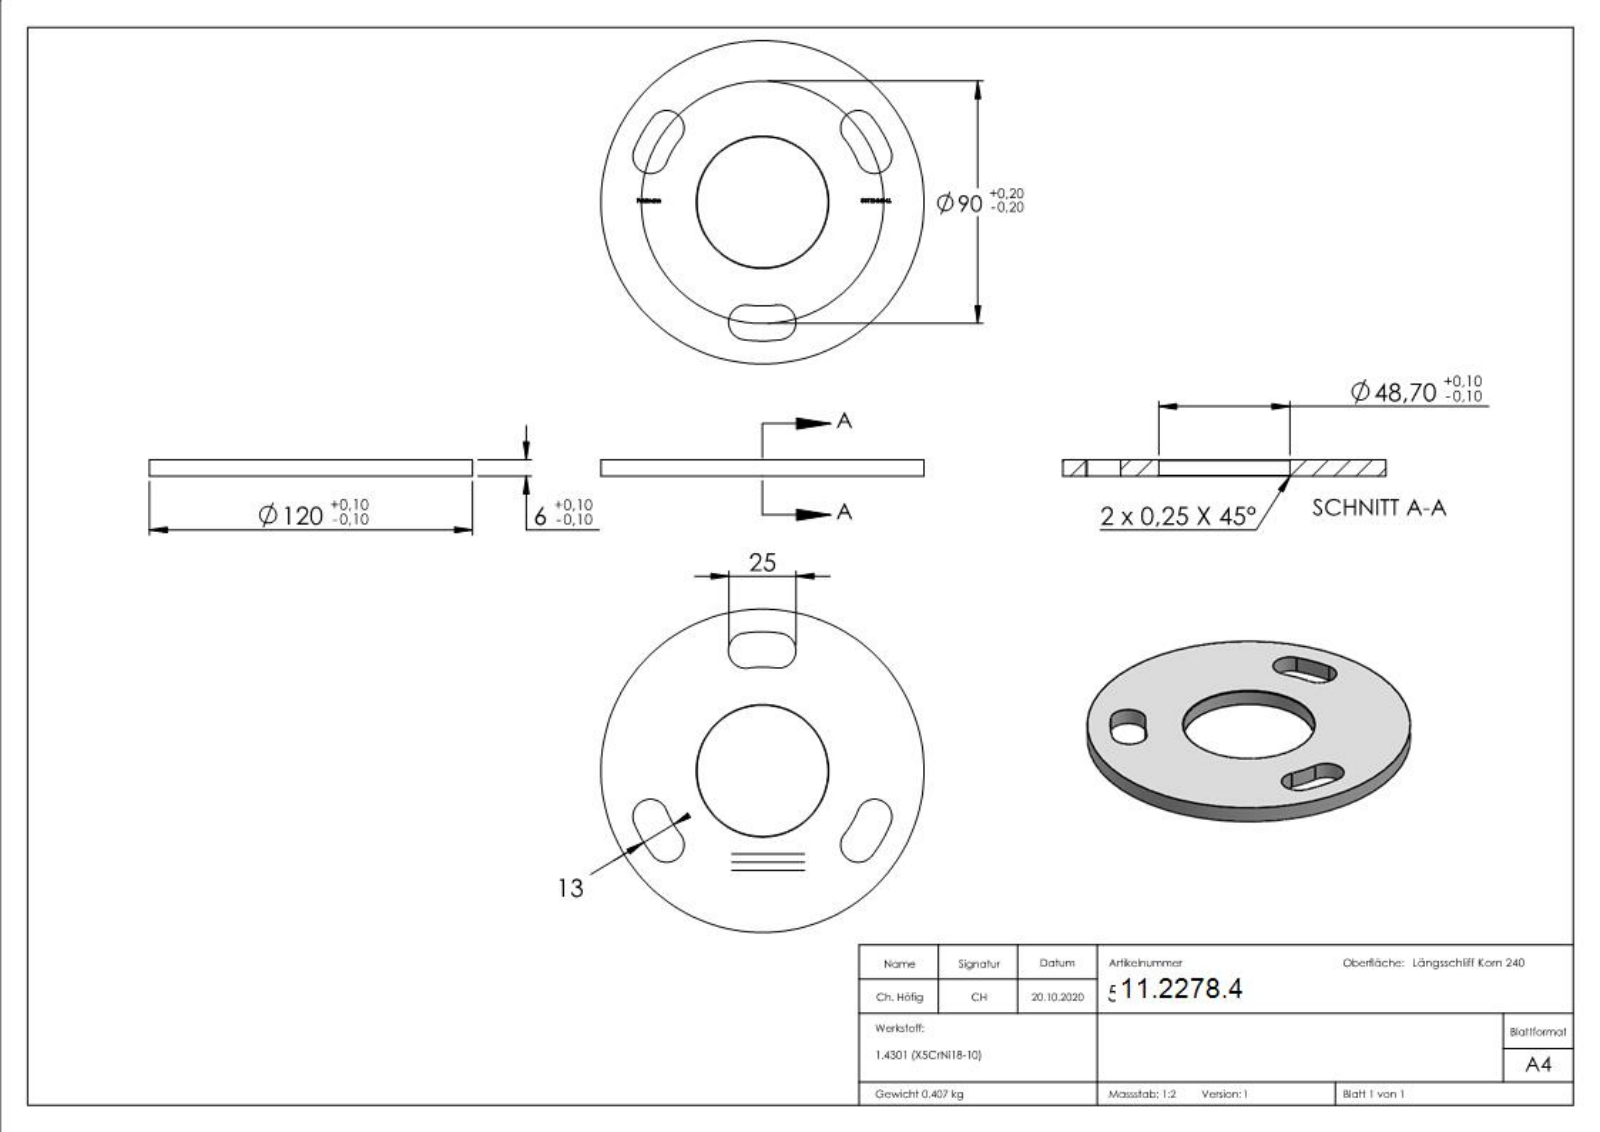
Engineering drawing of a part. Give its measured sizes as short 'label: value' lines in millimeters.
name: 54112-240-LL
written by: SolidWorks 2018 (CONFIG_CONTROL_DESIGN)
unit: mm
bodies: 1 solid, 259 faces (158 planar, 20 cylindrical, 81 other)
size: 120 × 120 × 6
volume: 51 466 mm³; area: 21 473 mm²
holes: 1× ⌀48.7
bosses: 1× ⌀120
rounds: 6× R6.5, 1× R38.5, 1× R51.5
face distances: 6, 5.9, 0.44, 90.62, 2.02, 0.88, 1.02, 1.19, 2.14, 83.58
